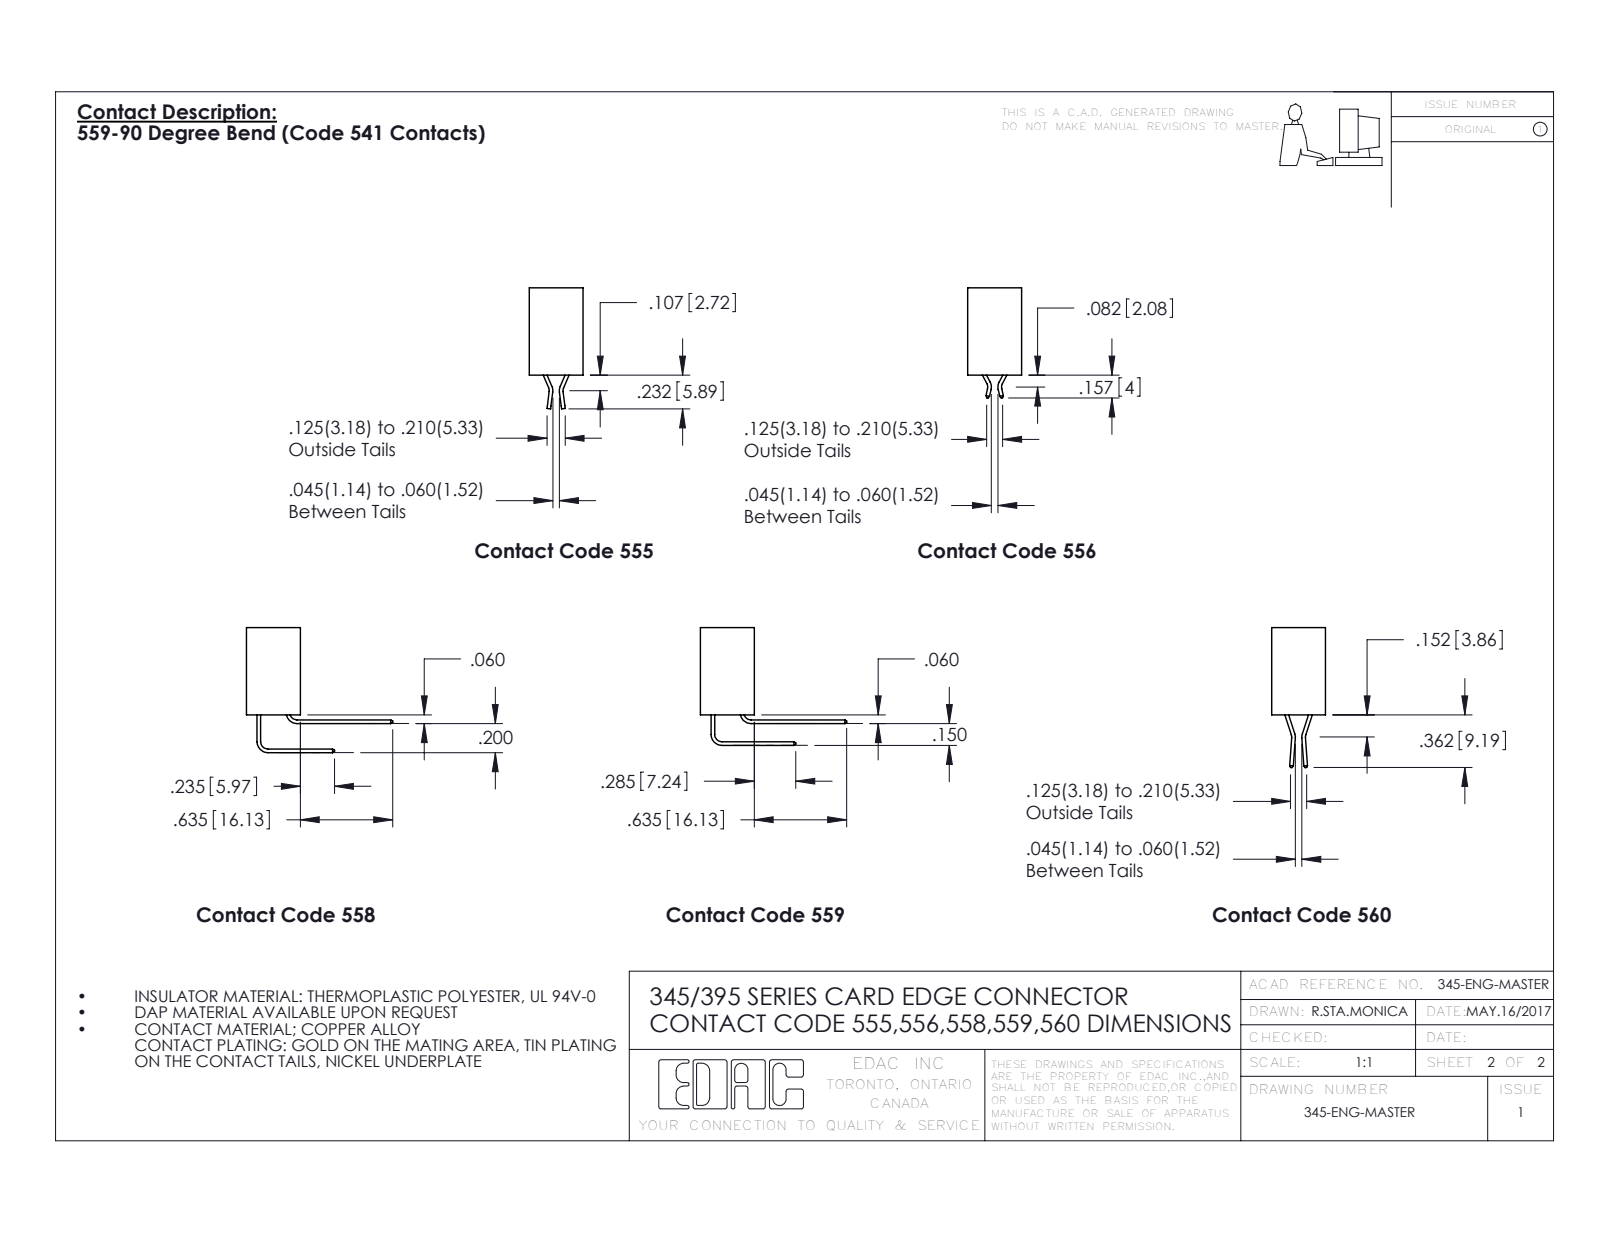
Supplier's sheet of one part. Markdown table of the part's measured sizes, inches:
| quantity | value |
| --- | --- |
| part name | 395-010-558-412; 345-292-001_558 Tail - 2; 345 Part_0.110 Offset - Side Mount |
| STEP written by | SolidWorks 2016 (CONFIG_CONTROL_DESIGN) |
| units | inches |
| bodies | 11 solids, 730 faces (504 planar, 226 cylindrical, 0 other) |
| overall size | 1.835 × 0.859 × 0.605 |
| volume | 0.246 in³ |
| surface area | 7.853 in² |
| round holes (diameter × count) | 0.128 × 2, 0.064 × 1 |
| partial cylindrical surfaces (radius × count) | 0.01 × 22, 0.006 × 20, 0.007 × 6, 0.031 × 6, 0.026 × 3, 0.031 × 2, 0.04 × 2, 0.014 × 1 |
| main face-to-face distances | 0.2, 0.072, 0.298, 0.37, 0.1, 0.098, 0.272, 0.025, 0.6, 0.06 |
| hole center spacings | 1.575 |
